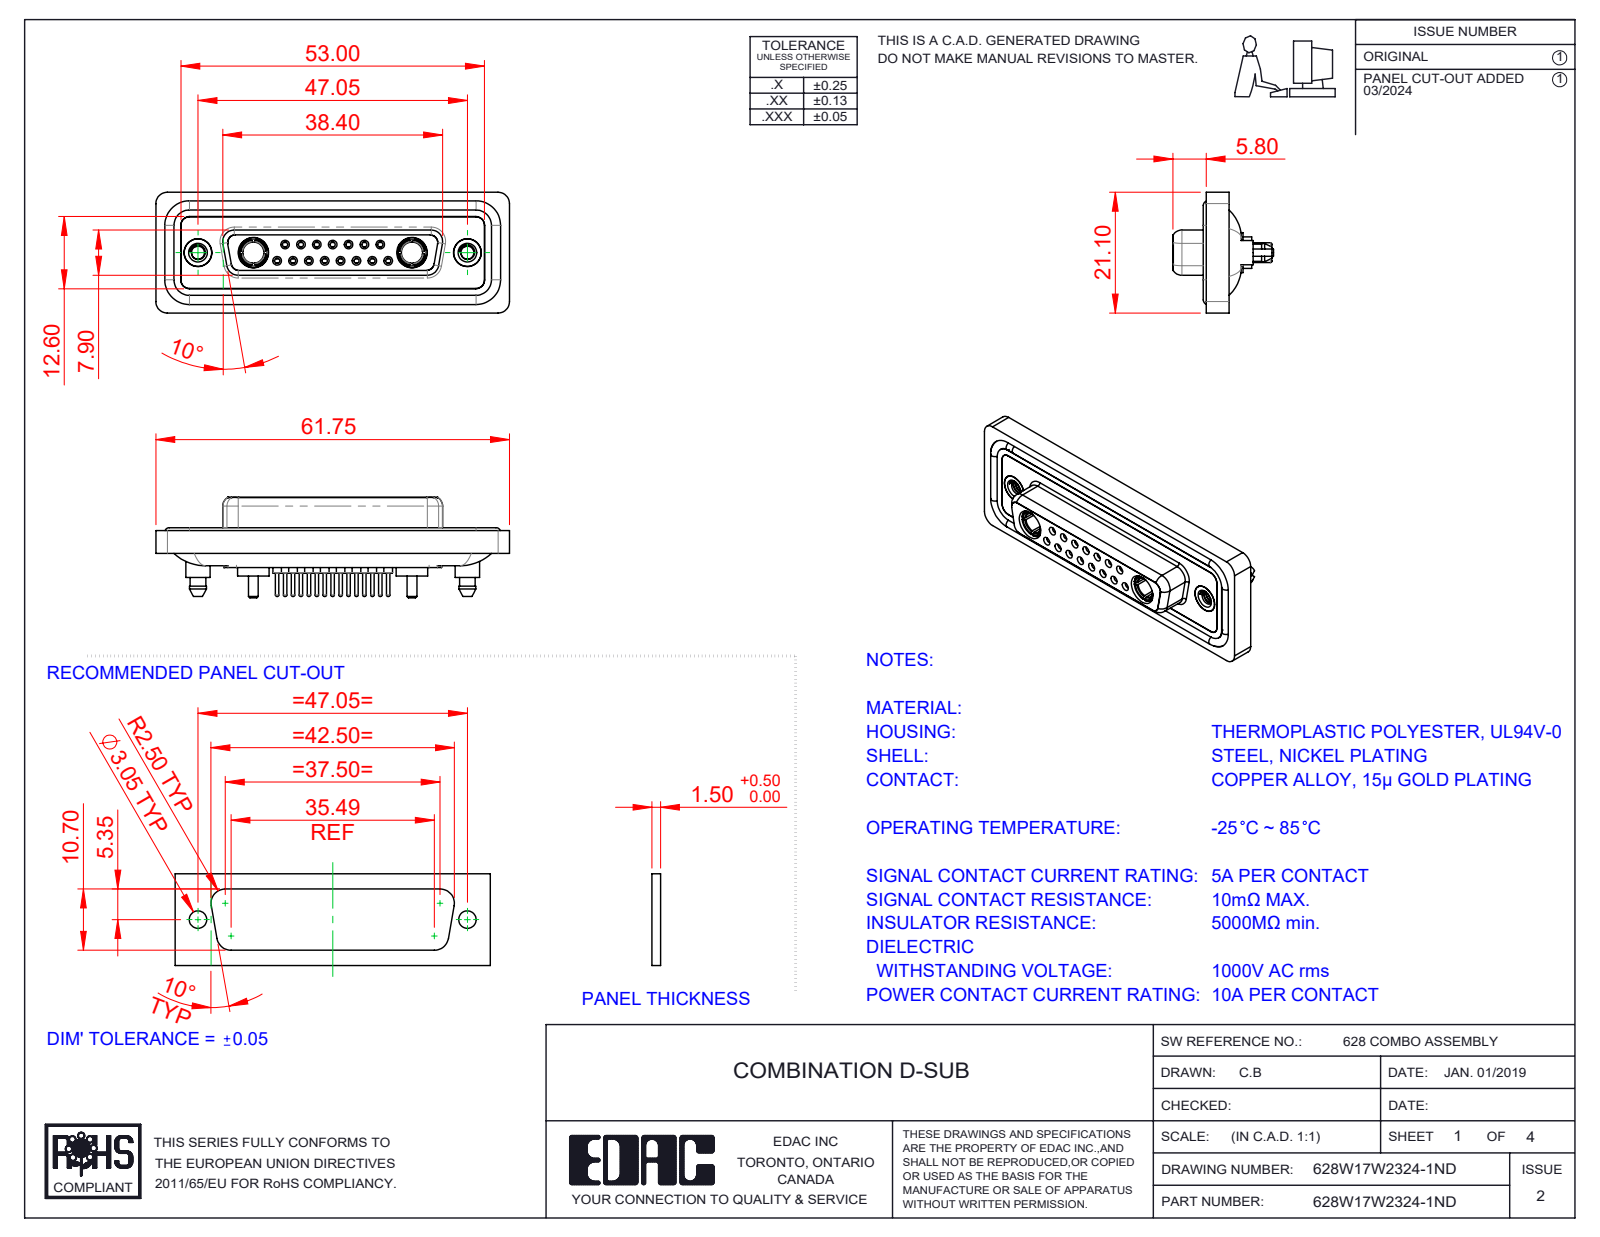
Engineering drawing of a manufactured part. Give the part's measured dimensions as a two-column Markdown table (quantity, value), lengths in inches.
| quantity | value |
| --- | --- |
| part name | 628Combo Contact Row 1_24; 628Combo Housing_17W2; 628Combo Shell Front_25 Contacts; 628Combo Contact Row 2_24 (+5 more) |
| STEP written by | SolidWorks 2023 (CONFIG_CONTROL_DESIGN) |
| units | inches |
| bodies | 26 solids, 1425 faces (404 planar, 567 cylindrical, 454 other) |
| overall size | 2.431 × 0.831 × 0.691 |
| volume | 0.514 in³ |
| surface area | 21.96 in² |
| round holes (diameter × count) | 0.035 × 15, 0.043 × 15, 0.059 × 15, 0.079 × 15, 0.063 × 8, 0.067 × 7, 0.191 × 4, 0.089 × 2, 0.146 × 2, 0.157 × 2, 0.159 × 2, 0.197 × 2 |
| round bosses / shafts (diameter × count) | 0.087 × 15, 0.024 × 15, 0.063 × 11, 0.217 × 2, 0.213 × 2, 0.205 × 2, 0.195 × 2, 0.195 × 2 |
| partial cylindrical surfaces (radius × count) | 0.059 × 24, 0.079 × 18, 0.063 × 10, 0.053 × 8, 0.01 × 4, 0.02 × 4, 0.024 × 4, 0.026 × 4 |
| main face-to-face distances | 0.016, 0.071, 0.293, 0.222, 0.26, 0.02, 0.278, 0.063, 0.114, 0.043 |
| hole center spacings | 0.124, 0.109, 0.327, 0.218, 0.198, 0.198, 0.295, 0.436 |
